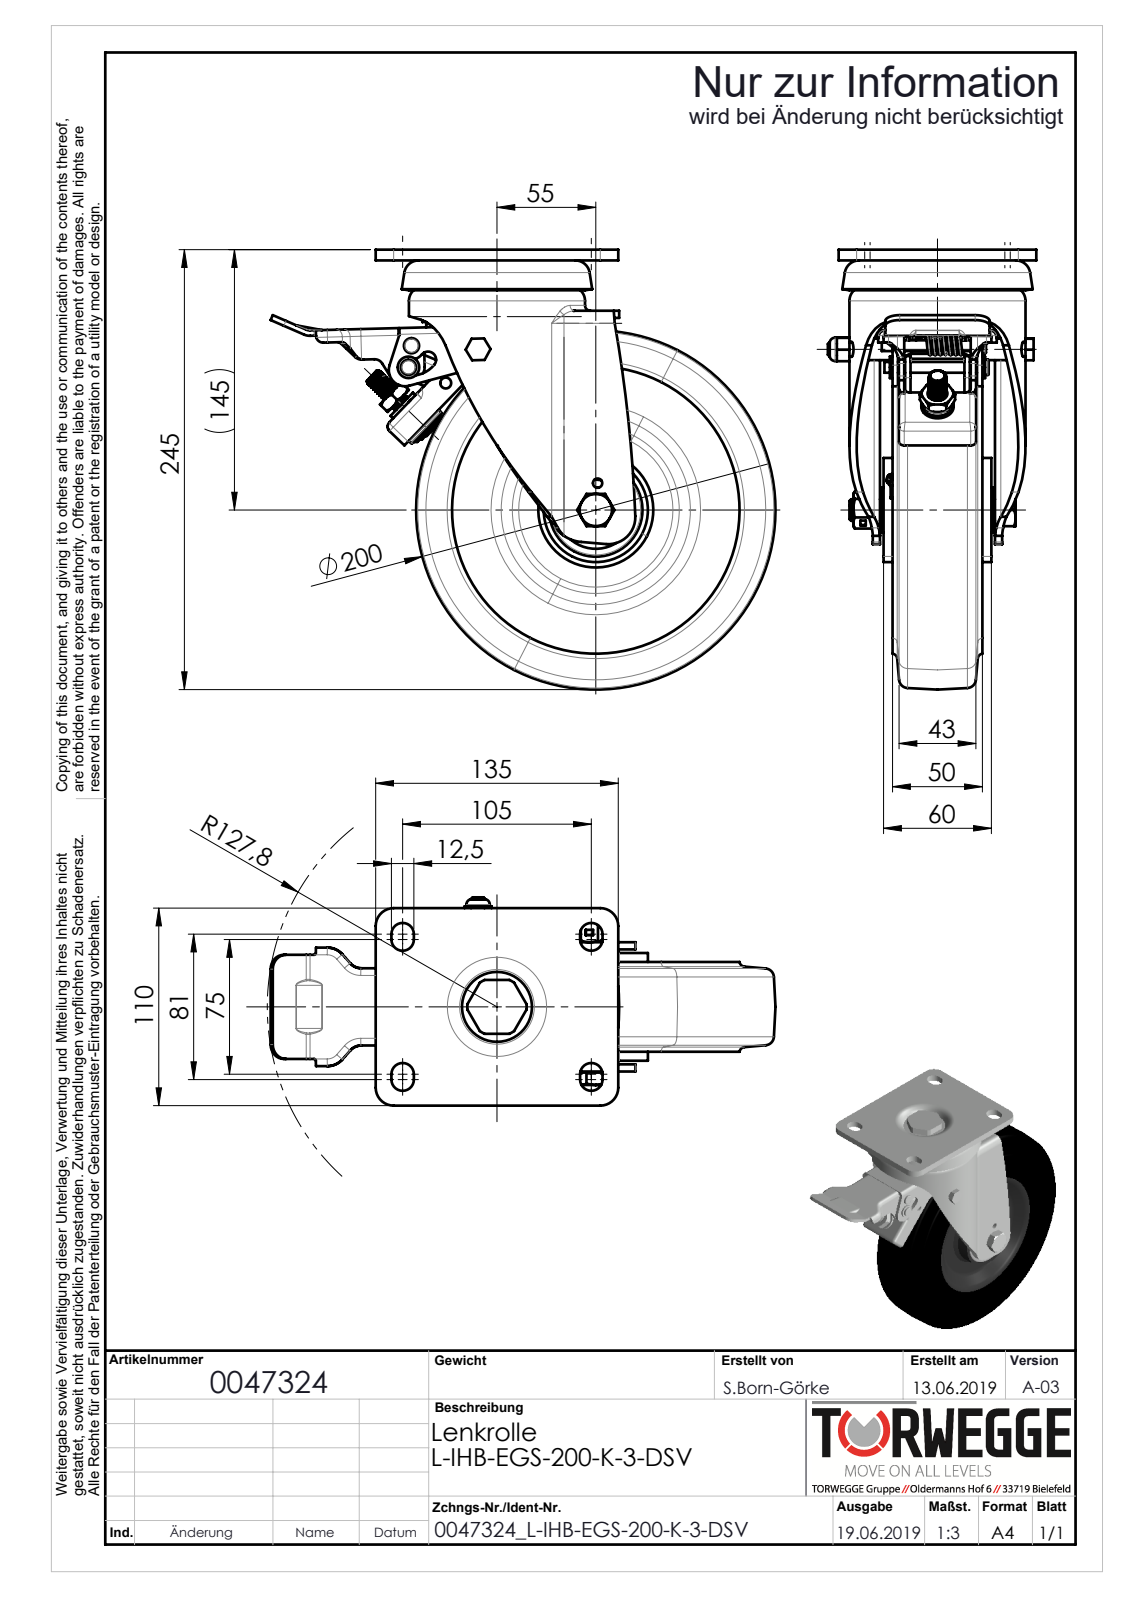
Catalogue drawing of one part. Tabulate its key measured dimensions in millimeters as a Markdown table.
| quantity | value |
| --- | --- |
| part name | 0047324_L-IHB-EGS-200-K-3-DSV_(A-03) |
| STEP written by | SolidWorks 2018 (AUTOMOTIVE_DESIGN) |
| units | millimeters |
| bodies | 26 solids, 1201 faces (363 planar, 534 cylindrical, 304 other) |
| overall size | 280.97 × 245 × 116 |
| volume | 1 883 000 mm³ |
| surface area | 264 789 mm² |
| round holes (diameter × count) | 6.1 × 3, 4 × 2, 8.1 × 2, 2 × 1, 3 × 1, 4.5 × 1, 5.2 × 1, 6.5 × 1, 7.8 × 1, 8 × 1, 8.5 × 1, 10.2 × 1 |
| round bosses / shafts (diameter × count) | 18 × 2, 12 × 2, 8.5 × 2, 6 × 2, 98 × 1, 48 × 1, 33 × 1, 25 × 1 |
| partial cylindrical surfaces (radius × count) | 3 × 31, 1 × 25, 6.25 × 10, 0.5 × 9, 3.5 × 9, 4 × 9, 8 × 7, 11 × 6 |
| main face-to-face distances | 3, 6, 7, 50, 40, 4, 11, 61, 10, 47 |
| hole center spacings | 12.16, 15.01, 22.5, 25.99, 28.19, 37.13, 40.02, 99.86 |
